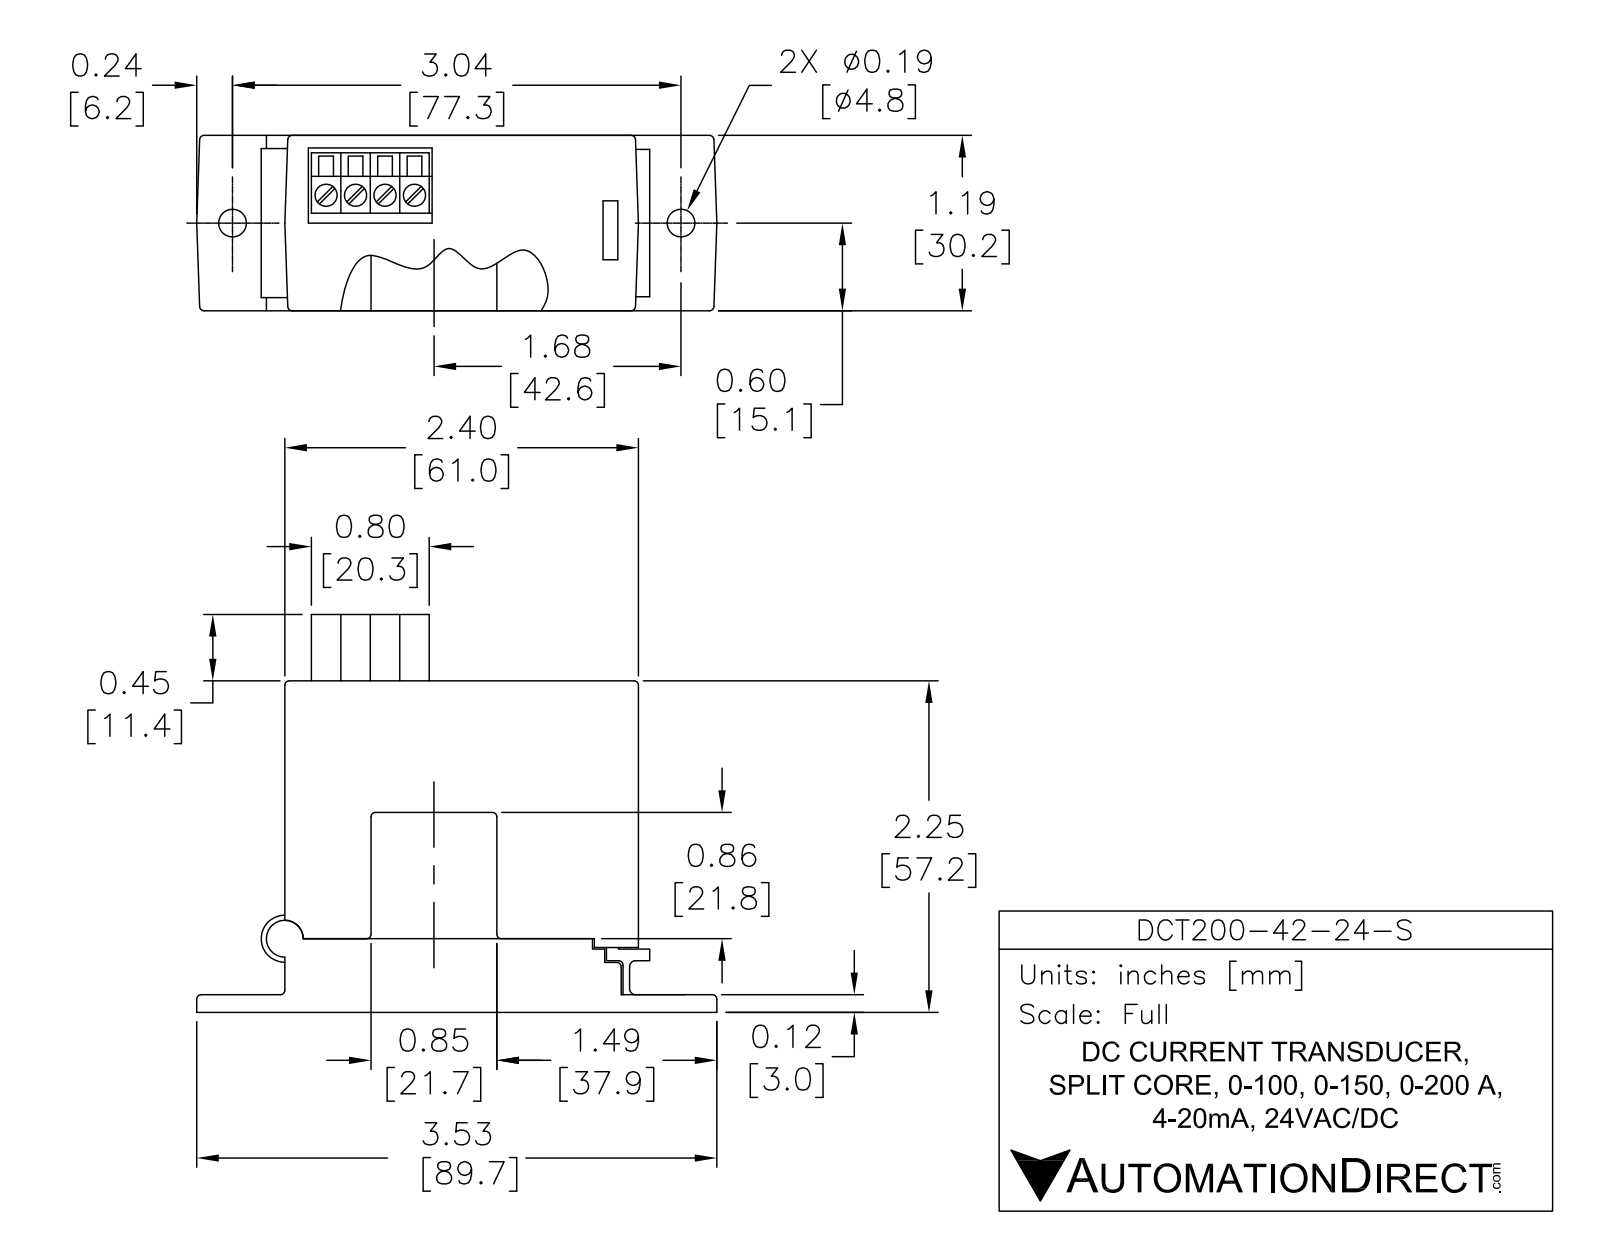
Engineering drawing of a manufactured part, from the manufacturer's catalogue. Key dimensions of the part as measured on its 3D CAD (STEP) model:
Part name (STEP PRODUCT): DCT200-42-24-S
STEP written by: SolidWorks 2017 (AUTOMOTIVE_DESIGN)
Units: inches
Bodies: 4 solids, 158 faces (100 planar, 50 cylindrical, 8 other)
Overall size (bounding box): 3.531 × 2.7 × 1.189
Volume: 5.725 in³ · Surface area: 35.03 in²
Round holes (diameter × count): ⌀0.157 ×4, ⌀0.188 ×2, ⌀0.26 ×1
Round bosses / shafts (diameter × count): ⌀0.25 ×1
Partial cylindrical surfaces — rounded edges, fillets, slot ends (radius × count): R0.03 ×22, R0.16 ×1, R0.17 ×1
Main face-to-face distances: 1.189, 2.252, 0.5, 1.752, 2.399, 0.505, 1.747, 0.118, 0.382, 0.387
Hole centre spacings: 0.197, 0.398, 0.201, 0.596, 0.632, 0.822, 1.019, 1.213
